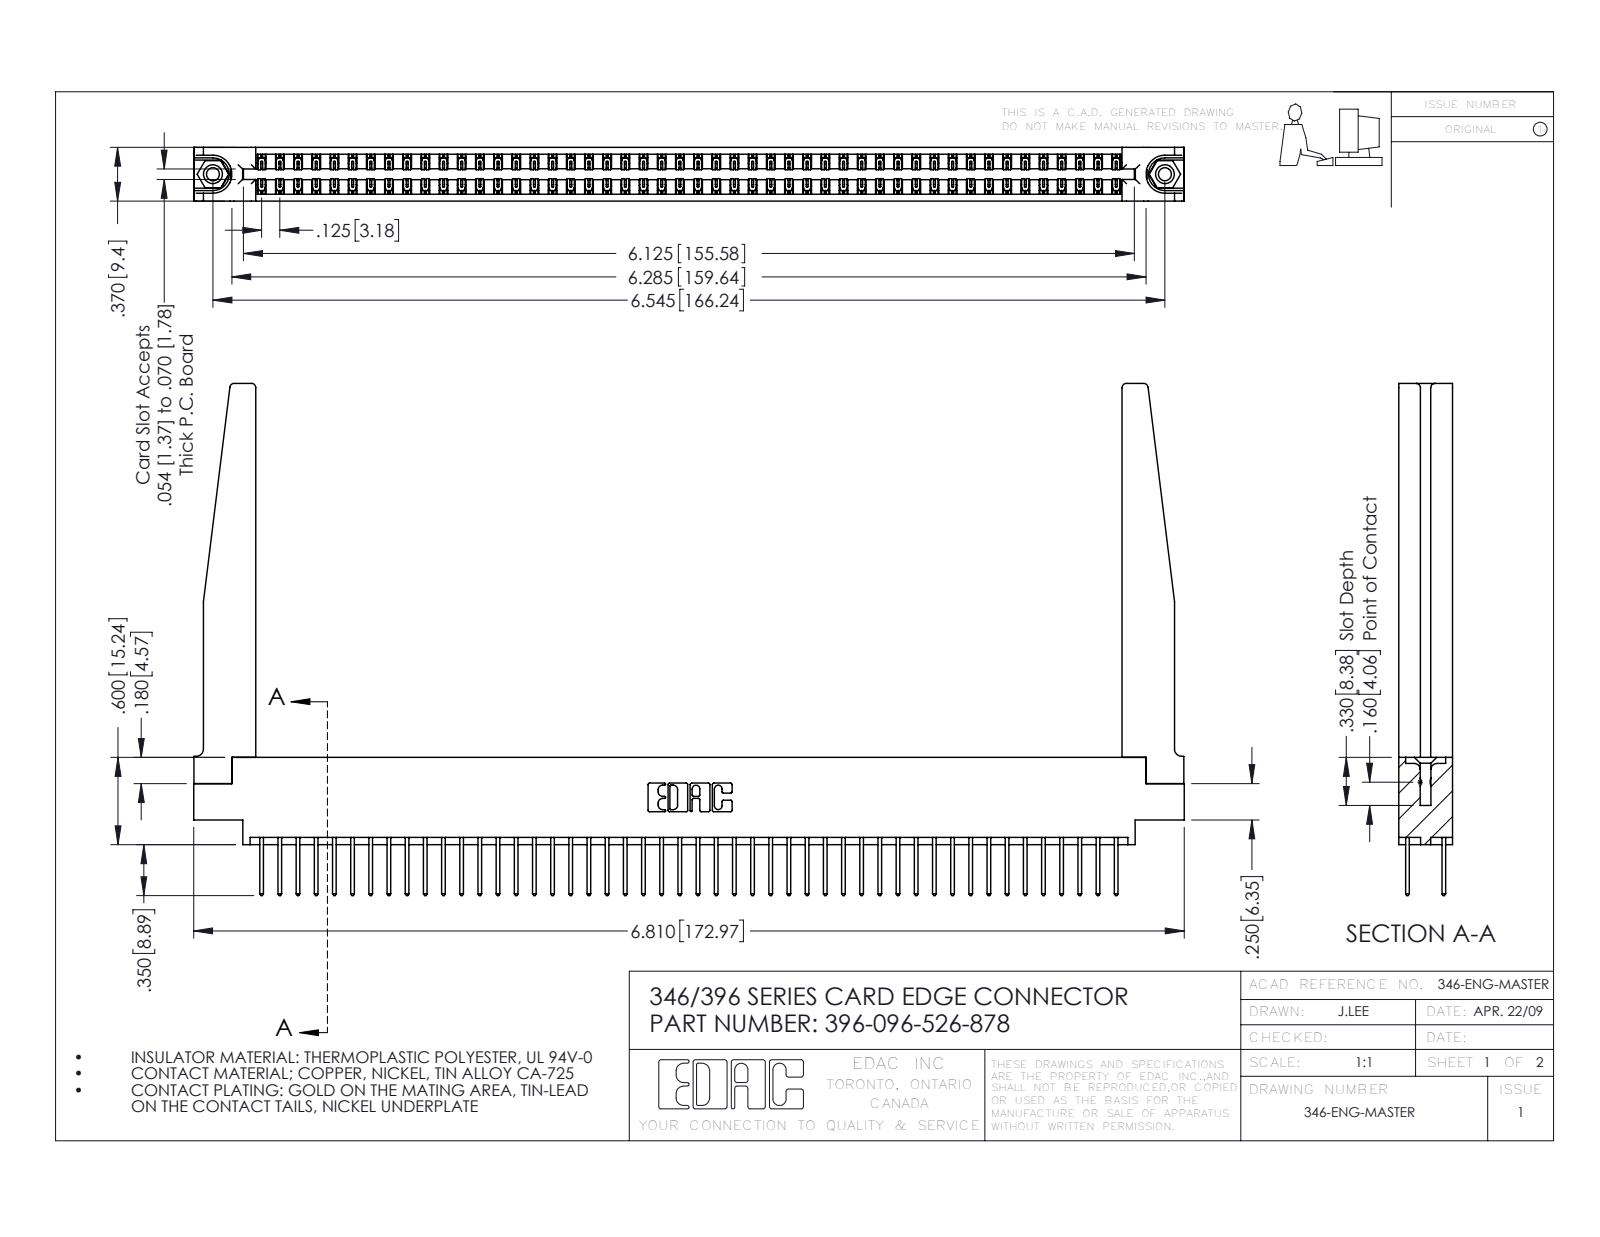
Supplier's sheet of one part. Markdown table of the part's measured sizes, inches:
| quantity | value |
| --- | --- |
| part name | 396-096-526-878; 345-292-001_345-293-126; 346-220-078_345-220-078; 346 Part_0.170 Offset - 0.156 Dia-TH (+1 more) |
| STEP written by | SolidWorks 2016 (CONFIG_CONTROL_DESIGN) |
| units | inches |
| bodies | 101 solids, 5352 faces (3582 planar, 1718 cylindrical, 52 other) |
| overall size | 6.81 × 3.52 × 0.37 |
| volume | 1.454 in³ |
| surface area | 47.69 in² |
| round holes (diameter × count) | 0.089 × 2, 0.125 × 2, 0.156 × 2, 0.064 × 1 |
| round bosses / shafts (diameter × count) | 0.155 × 2 |
| partial cylindrical surfaces (radius × count) | 0.006 × 144, 0.01 × 96, 0.01 × 22, 0.03 × 8, 0.007 × 6, 0.031 × 6, 0.026 × 3, 0.014 × 2 |
| main face-to-face distances | 0.048, 0.322, 0.37, 0.072, 0.25, 0.298, 0.025, 0.148, 0.15, 0.275 |
| hole center spacings | 0.246, 6.336, 6.545 |
